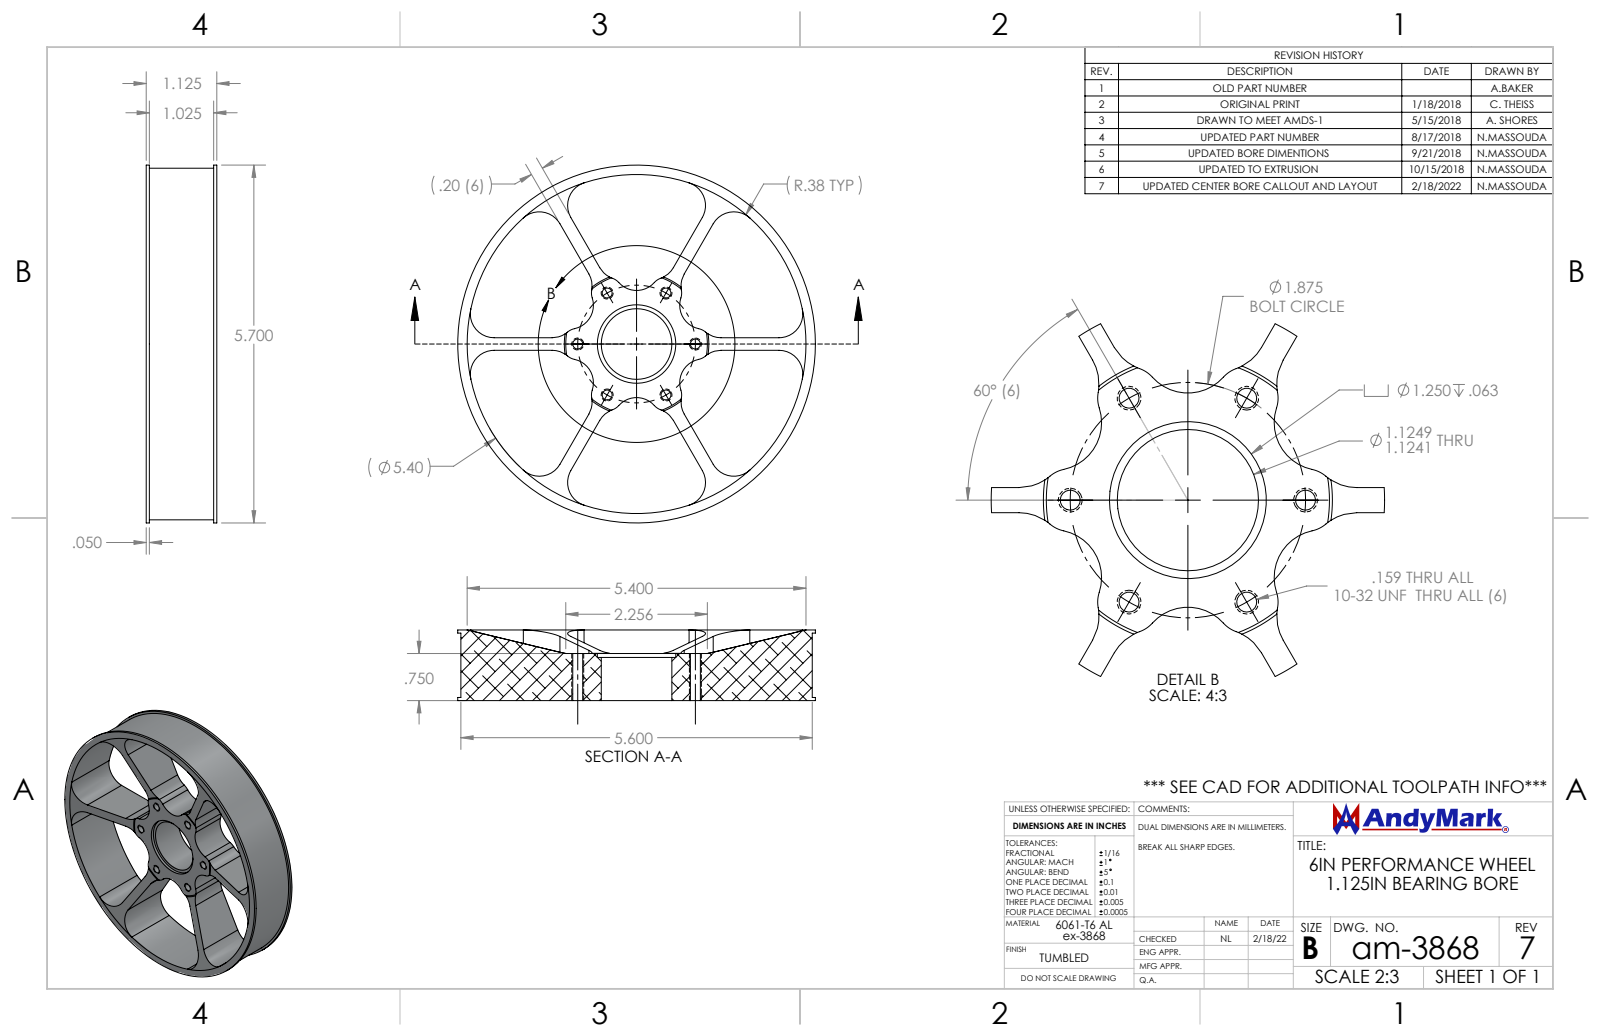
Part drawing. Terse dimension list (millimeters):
name: am-3868 6in Performance Wheel Bearing Bore
written by: SolidWorks 2021 (CONFIG_CONTROL_DESIGN)
unit: mm
bodies: 1 solid, 112 faces (18 planar, 80 cylindrical, 14 other)
size: 144.8 × 144.8 × 28.6
volume: 97 440 mm³; area: 50 160 mm²
holes: 6× ⌀4, 1× ⌀28.6, 1× ⌀31.8
bosses: 1× ⌀144.8, 1× ⌀142.2
rounds: 30× R9.7, 6× R6.4, 1× R68.6
face distances: 5.1, 28.6, 9.5, 19.1, 1.3, 27.3, 8.3, 26, 17.8, 11.1
hole spacings: 23.8, 41.2, 47.6, 23.8
